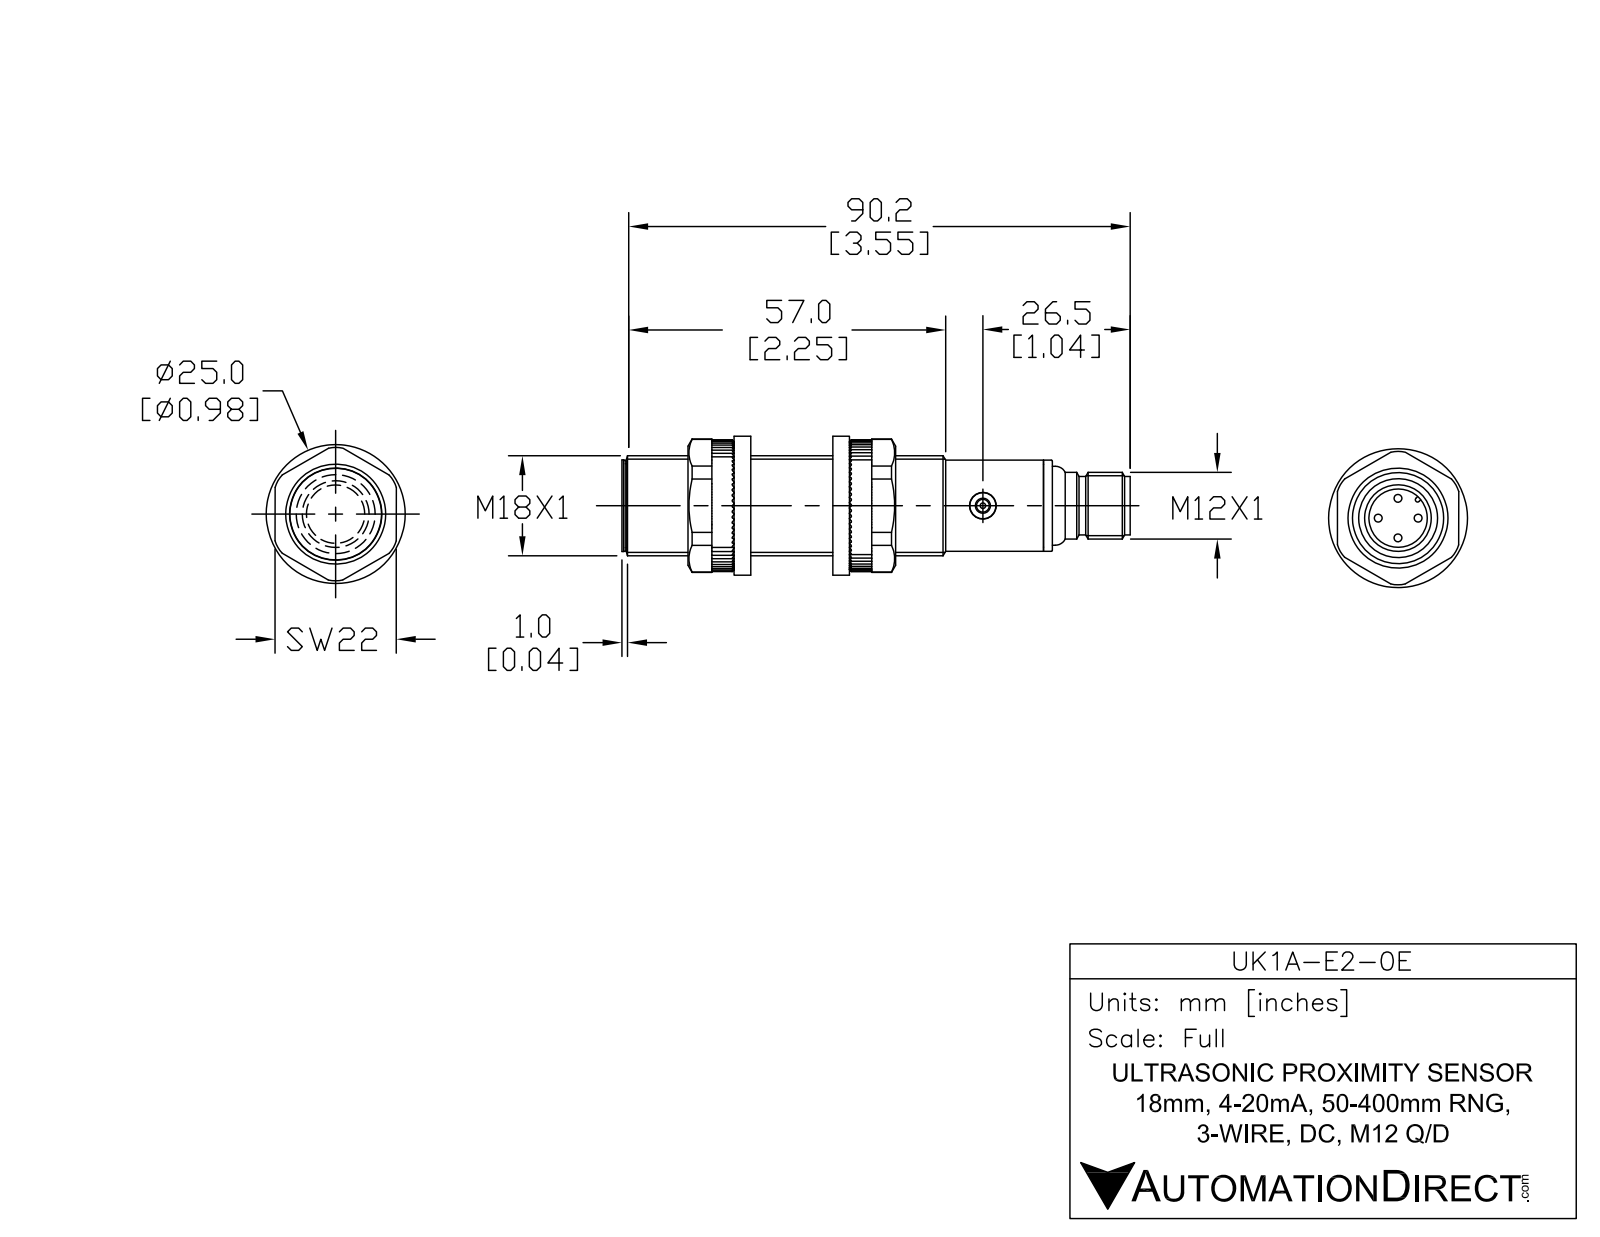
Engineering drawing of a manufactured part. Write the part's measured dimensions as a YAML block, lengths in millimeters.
part_name: "UK1A-E2-0E"
step_written_by: "SolidWorks 2017 (AUTOMOTIVE_DESIGN)"
units: millimeters
bodies: {solids: 6, faces: 106, planar: 21, cylindrical: 48, other: 37}
overall_size: [91.6, 18, 18]
volume: 19700
surface_area: 6890
round_holes:
  - {diameter: 2.7, count: 1}
  - {diameter: 4.7, count: 1}
  - {diameter: 7, count: 1}
  - {diameter: 8.3, count: 1}
  - {diameter: 9.5, count: 1}
round_bosses_or_shafts:
  - {diameter: 1, count: 4}
  - {diameter: 18, count: 1}
  - {diameter: 16.6, count: 1}
  - {diameter: 16.4, count: 1}
  - {diameter: 15.8, count: 1}
  - {diameter: 14.2, count: 1}
  - {diameter: 12, count: 1}
  - {diameter: 10.5, count: 1}
partial_cylinders:
  - {radius: 0.6, count: 1}
face_to_face_distances: [75.1, 1, 76.1, 0.9, 76, 1.1, 4, 77.6, 77.5, 76.6]
